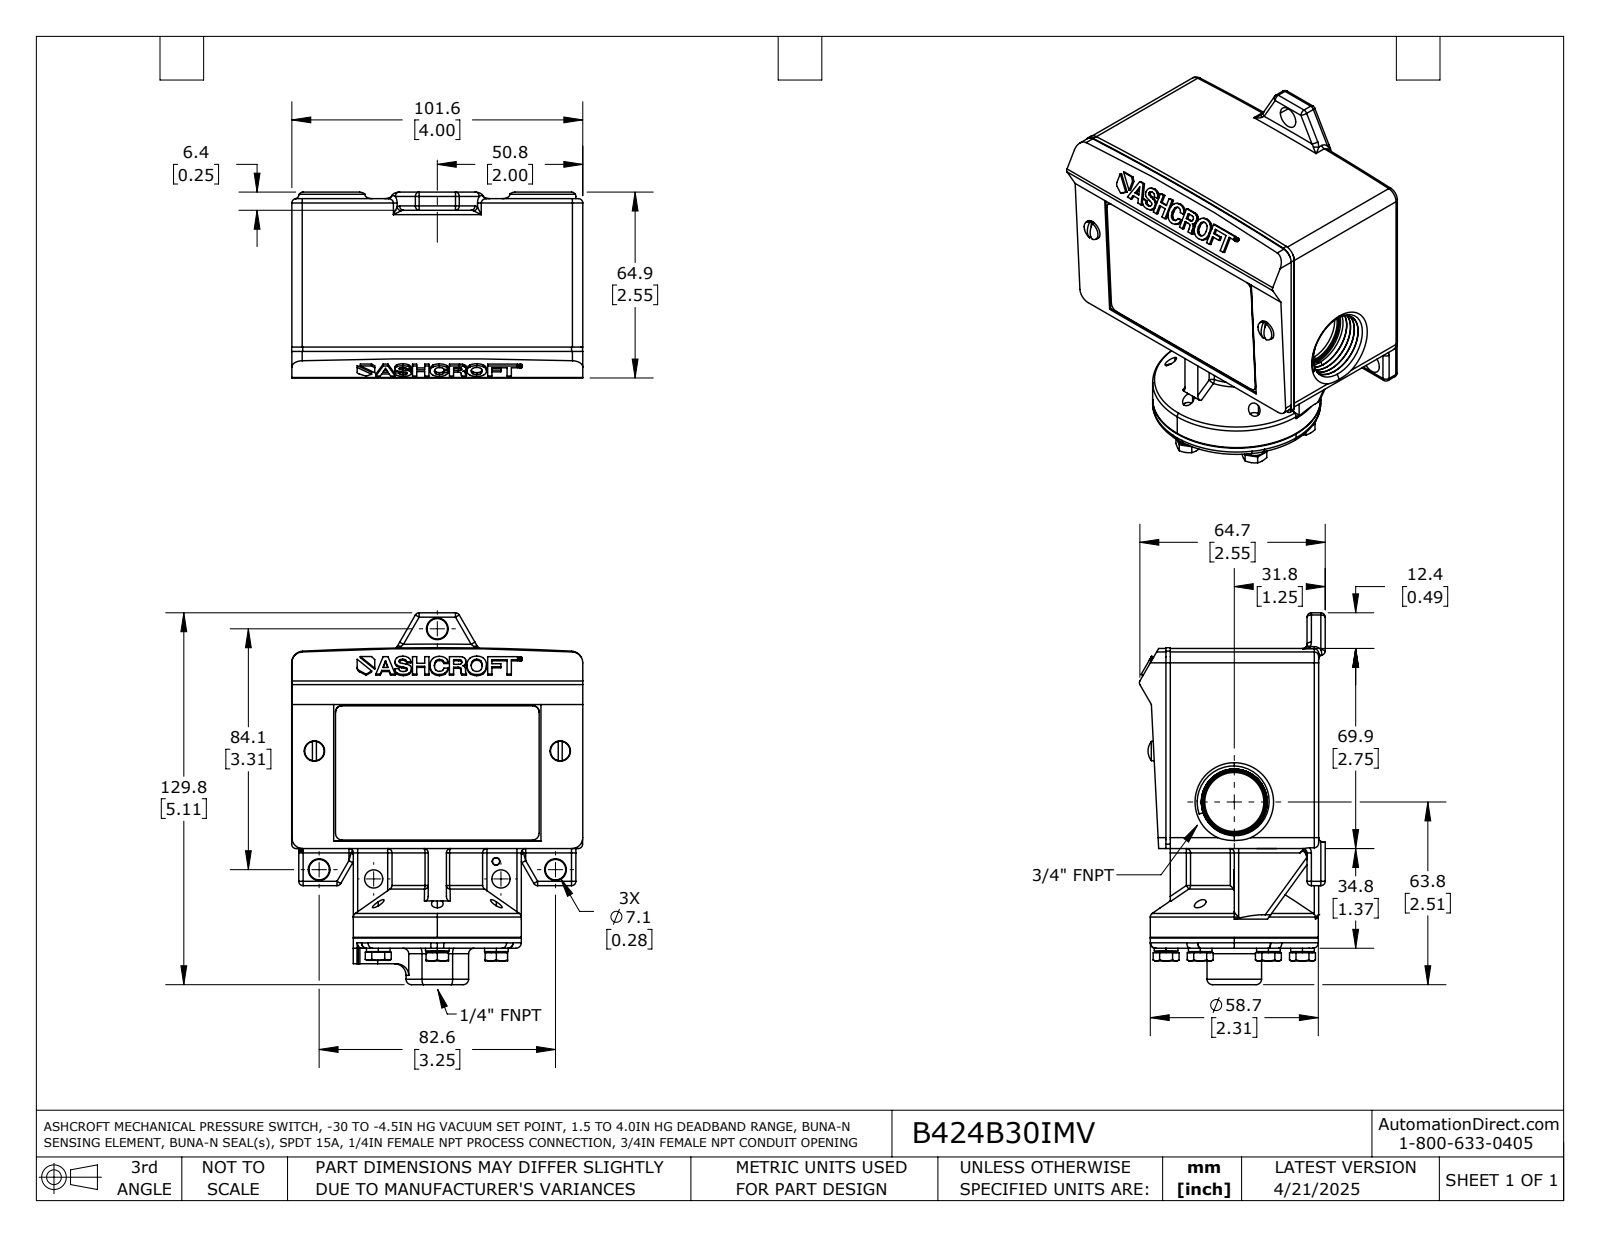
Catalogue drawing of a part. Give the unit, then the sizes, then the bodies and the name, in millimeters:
Units: millimetres
Overall size (bounding box): 129.8 × 101.7 × 64.9
Round holes (diameter × count): ⌀4.1 ×6, ⌀4.9 ×5, ⌀5.3 ×5, ⌀4.7 ×4, ⌀7.1 ×2, ⌀11.6 ×1, ⌀20.6 ×1
Round bosses / shafts (diameter × count): ⌀8.3 ×6, ⌀7.1 ×6, ⌀4.8 ×5, ⌀6.9 ×2, ⌀6.4 ×2, ⌀58.7 ×1
Partial cylindrical surfaces — rounded edges, fillets, slot ends (radius × count): R1.5 ×92, R0.8 ×5, R1.9 ×4, R2.3 ×4, R3.8 ×4, R0.3 ×2, R2.4 ×2, R4.1 ×2
Main face-to-face distances: 101.6, 0.4, 34.8, 2.3, 99.3, 11.2, 90.4, 88.1, 8.9, 21.5
Hole centre spacings: 23.8, 41.2, 47.6, 23.8, 85.9
Volume: 468 200 mm³ · Surface area: 54 520 mm²
Bodies: 2 solids, 1259 faces (345 planar, 472 cylindrical, 442 other)
Part name (STEP PRODUCT): B424B30IMV
STEP written by: SolidWorks 2021 (AUTOMOTIVE_DESIGN)
